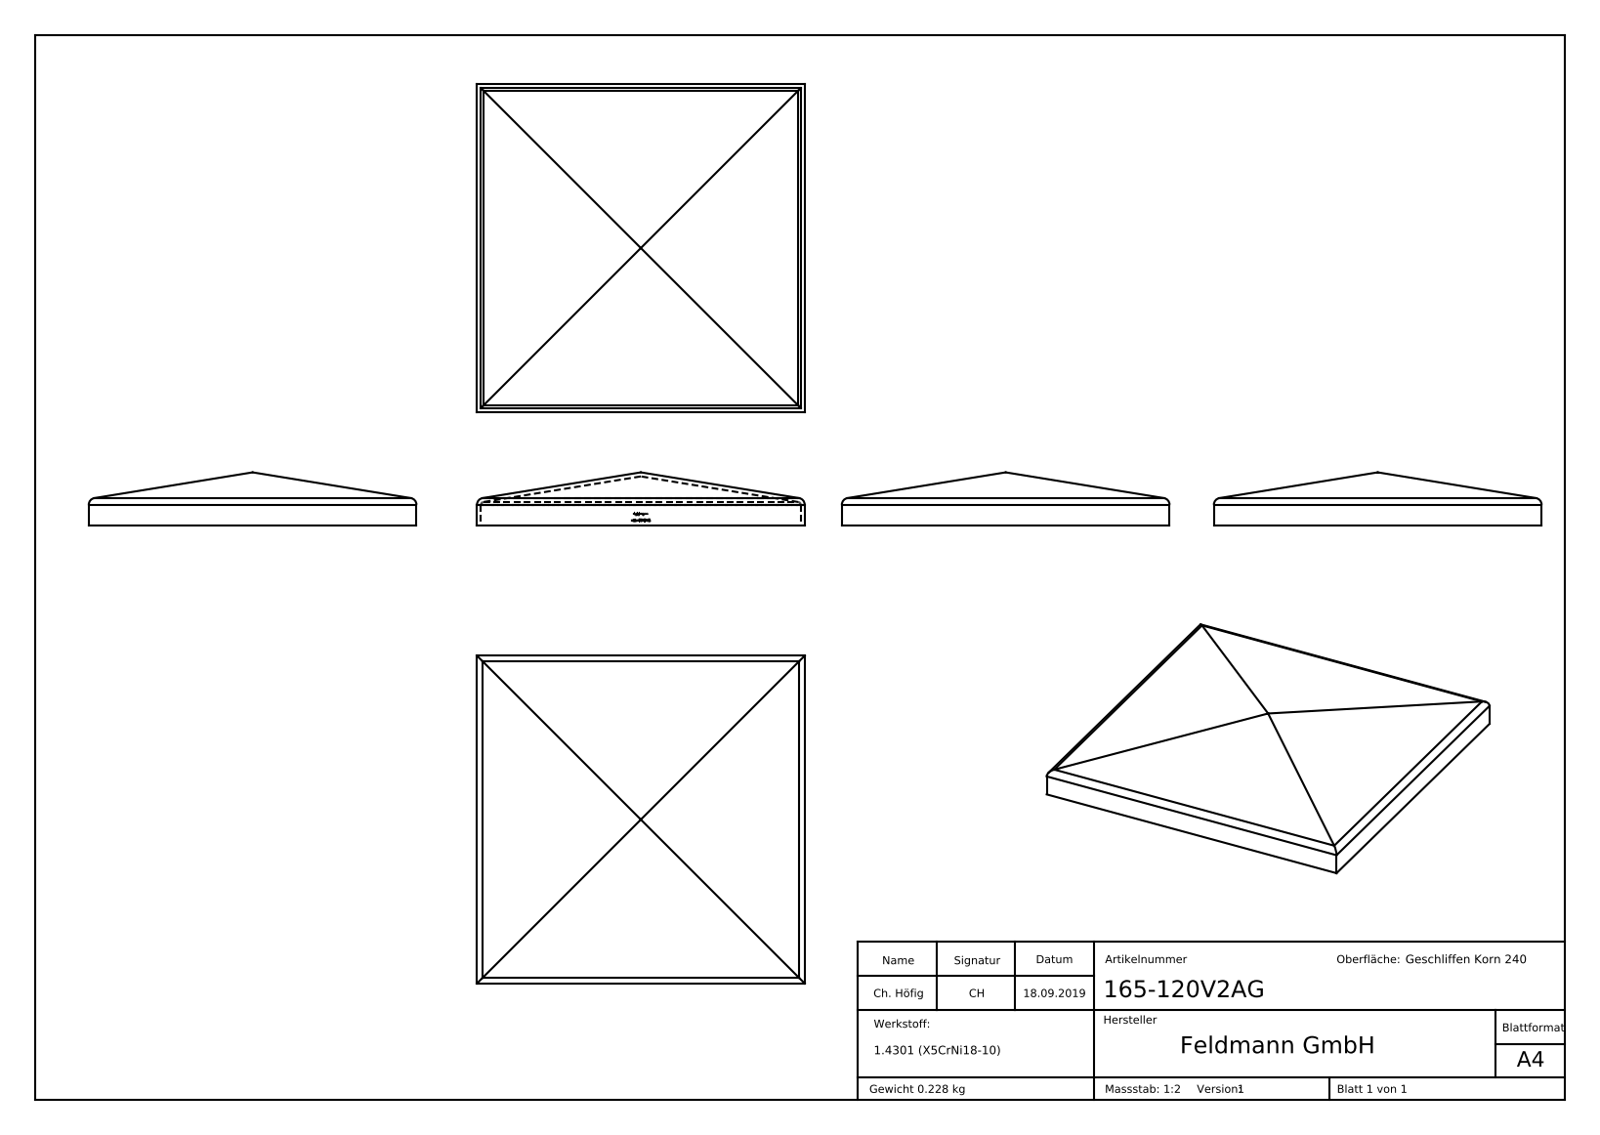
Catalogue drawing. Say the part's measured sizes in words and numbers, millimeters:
The part is named "165-120V2AG". Its 3-D file was written by "SolidWorks 2015 (CONFIG_CONTROL_DESIGN)". It is 1 solid with 262 faces: 155 planar, 12 cylindrical and 95 other. Overall it measures 123 by 123 by 20 millimeters. Its volume is 28 887 cubic millimeters and its surface area 39 258 square millimeters. Partial cylindrical surfaces (rounded edges, fillets, slot ends): 4 of radius 1, 4 of radius 2.5, 2 of radius 0.1. The main face-to-face distances are 1.5, 121.5, 123, 120, 1.4, 120.1, 121.6, 0.75, 2.2, 1.96.
